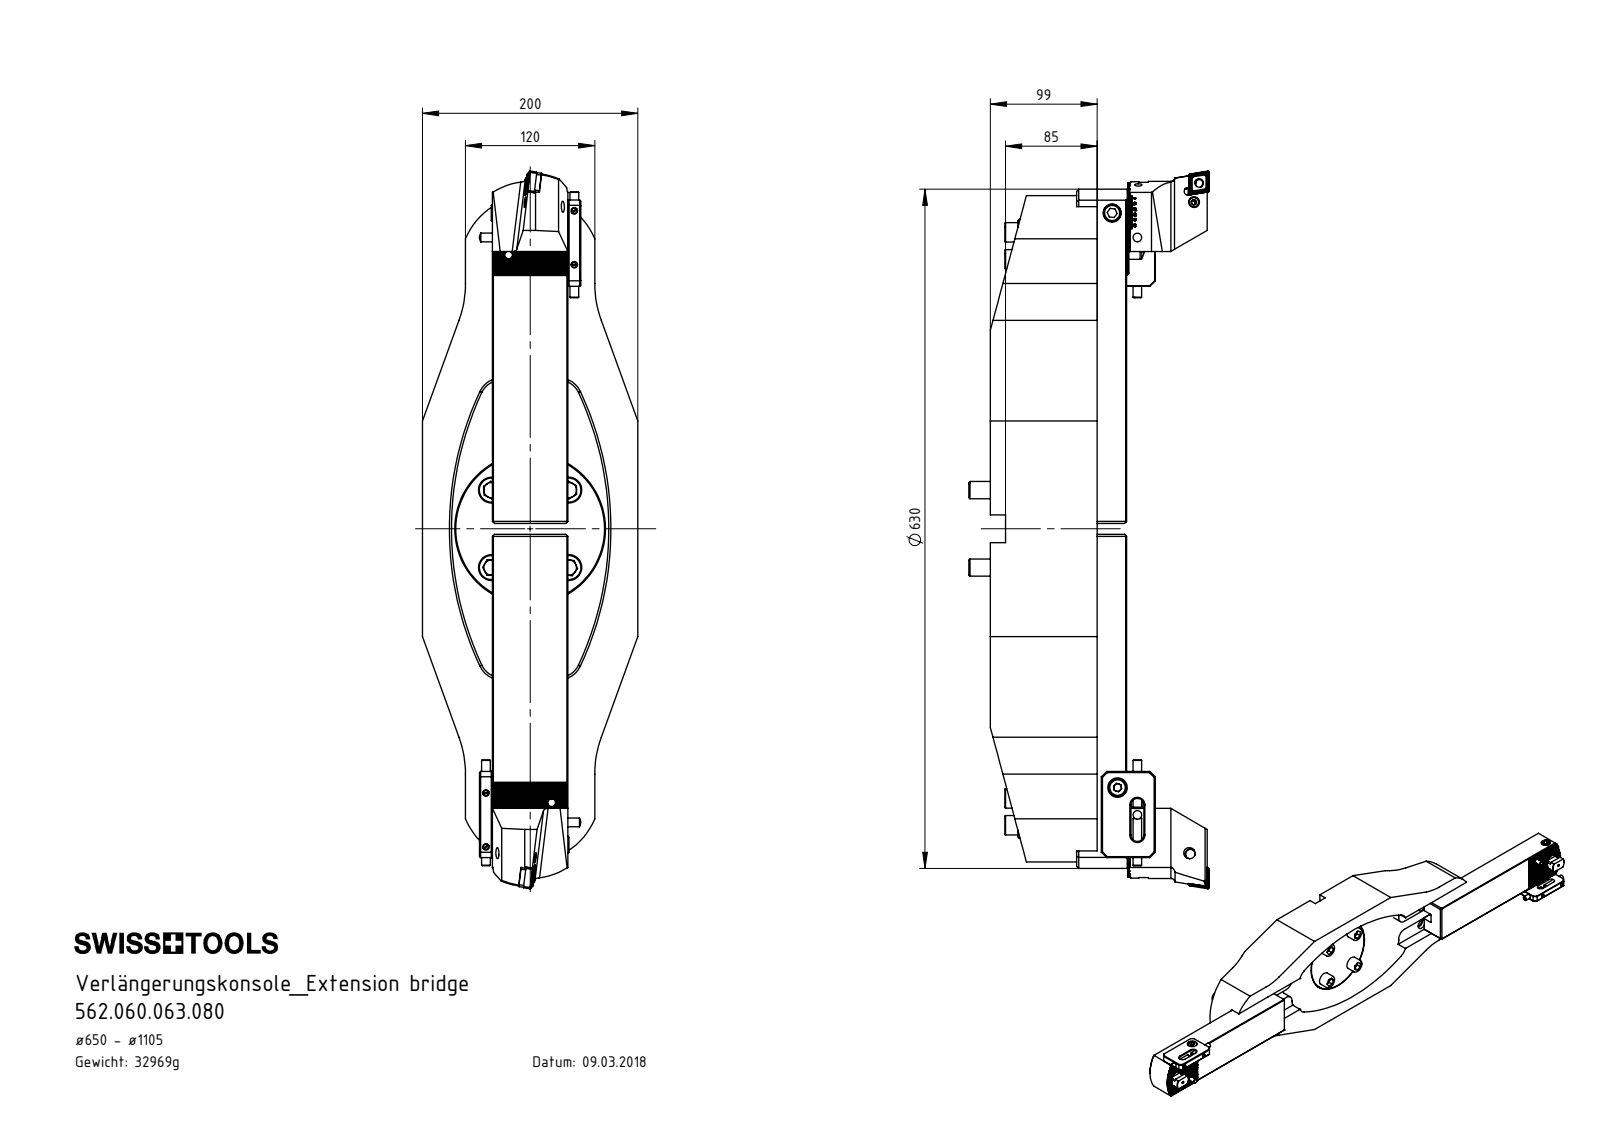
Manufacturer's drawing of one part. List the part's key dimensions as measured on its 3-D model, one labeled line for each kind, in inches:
Part name (STEP PRODUCT): ISO 8734 - 8 x 20 m6; DIN 7984 - M10 x 16; VK3-ER1.001.005_A; ISO 4028 - M8 x 35 (+8 more)
STEP written by: SolidWorks 2017 (CONFIG_CONTROL_DESIGN)
Units: inches
Bodies: 86 solids, 3665 faces (1810 planar, 950 cylindrical, 905 other)
Overall size (bounding box): 26.204 × 8.788 × 7.874
Volume: 524.6 in³ · Surface area: 1 463 in²
Round holes (diameter × count): ⌀0.709 ×40, ⌀0.402 ×34, ⌀0.512 ×16, ⌀0.268 ×6, ⌀0.315 ×6, ⌀0.472 ×6, ⌀0.197 ×4, ⌀0.236 ×4, ⌀0.669 ×4, ⌀0.079 ×2, ⌀0.313 ×2, ⌀0.335 ×2
Round bosses / shafts (diameter × count): ⌀0.945 ×19, ⌀0.472 ×9, ⌀0.63 ×8, ⌀0.394 ×4, ⌀0.236 ×4, ⌀0.709 ×2, ⌀0.39 ×2, ⌀0.339 ×2
Partial cylindrical surfaces — rounded edges, fillets, slot ends (radius × count): R0.006 ×55, R0.079 ×20, R0.047 ×8, R0.071 ×8, R0.163 ×8, R0.866 ×8, R0.591 ×6, R2.559 ×6
Main face-to-face distances: 1.732, 0.787, 0.984, 2.362, 5.315, 2.559, 3.15, 3.898, 1.535, 0.748
Hole centre spacings: 0.984, 1.857, 1.575, 1.969, 2.521, 18.701, 18.767, 5.906
